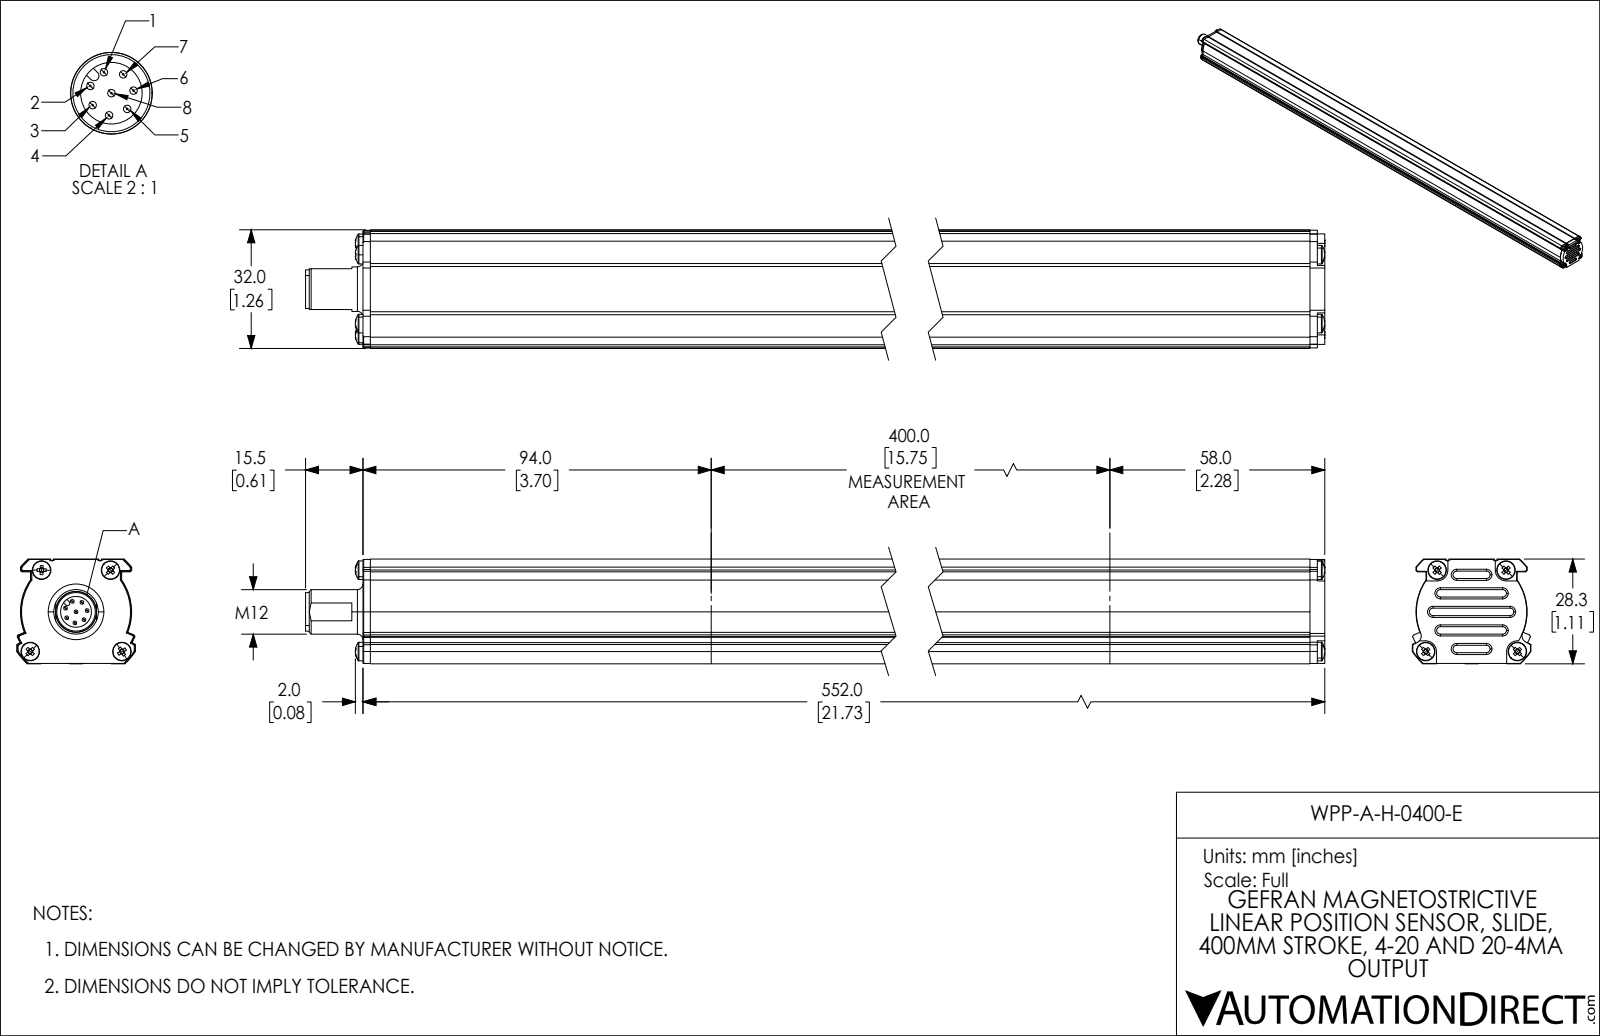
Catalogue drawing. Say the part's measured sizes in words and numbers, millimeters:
The part is named "WPP-A-H-0400-E". Its 3-D file was written by "SolidWorks 2021 (CONFIG_CONTROL_DESIGN)". It is 20 solids with 605 faces: 301 planar, 131 cylindrical and 173 other. Overall it measures 567.55 by 32 by 28.25 millimeters. Its volume is 440 402 cubic millimeters and its surface area 91 810 square millimeters. Round holes: 5 of diameter 2.6, 4 of diameter 2.3, 1 of diameter 7, 1 of diameter 8.3, 1 of diameter 9.4. Round bosses or shafts: 8 of diameter 1, 4 of diameter 5, 1 of diameter 12, 1 of diameter 10.4, 1 of diameter 9.55, 1 of diameter 8. Partial cylindrical surfaces (rounded edges, fillets, slot ends): 8 of radius 0.5, 4 of radius 2.9, 2 of radius 0.4, 2 of radius 1, 2 of radius 1.85, 1 of radius 0.65, 1 of radius 2, 1 of radius 14.9. The main face-to-face distances are 28, 28.25, 24.8, 24.55, 3.45, 3.7, 28.3, 546, 24.6, 2. The hole center spacings are 16.36, 14.6, 22.17, 30.85, 18.6, 22.16, 24.75, 24.76.
